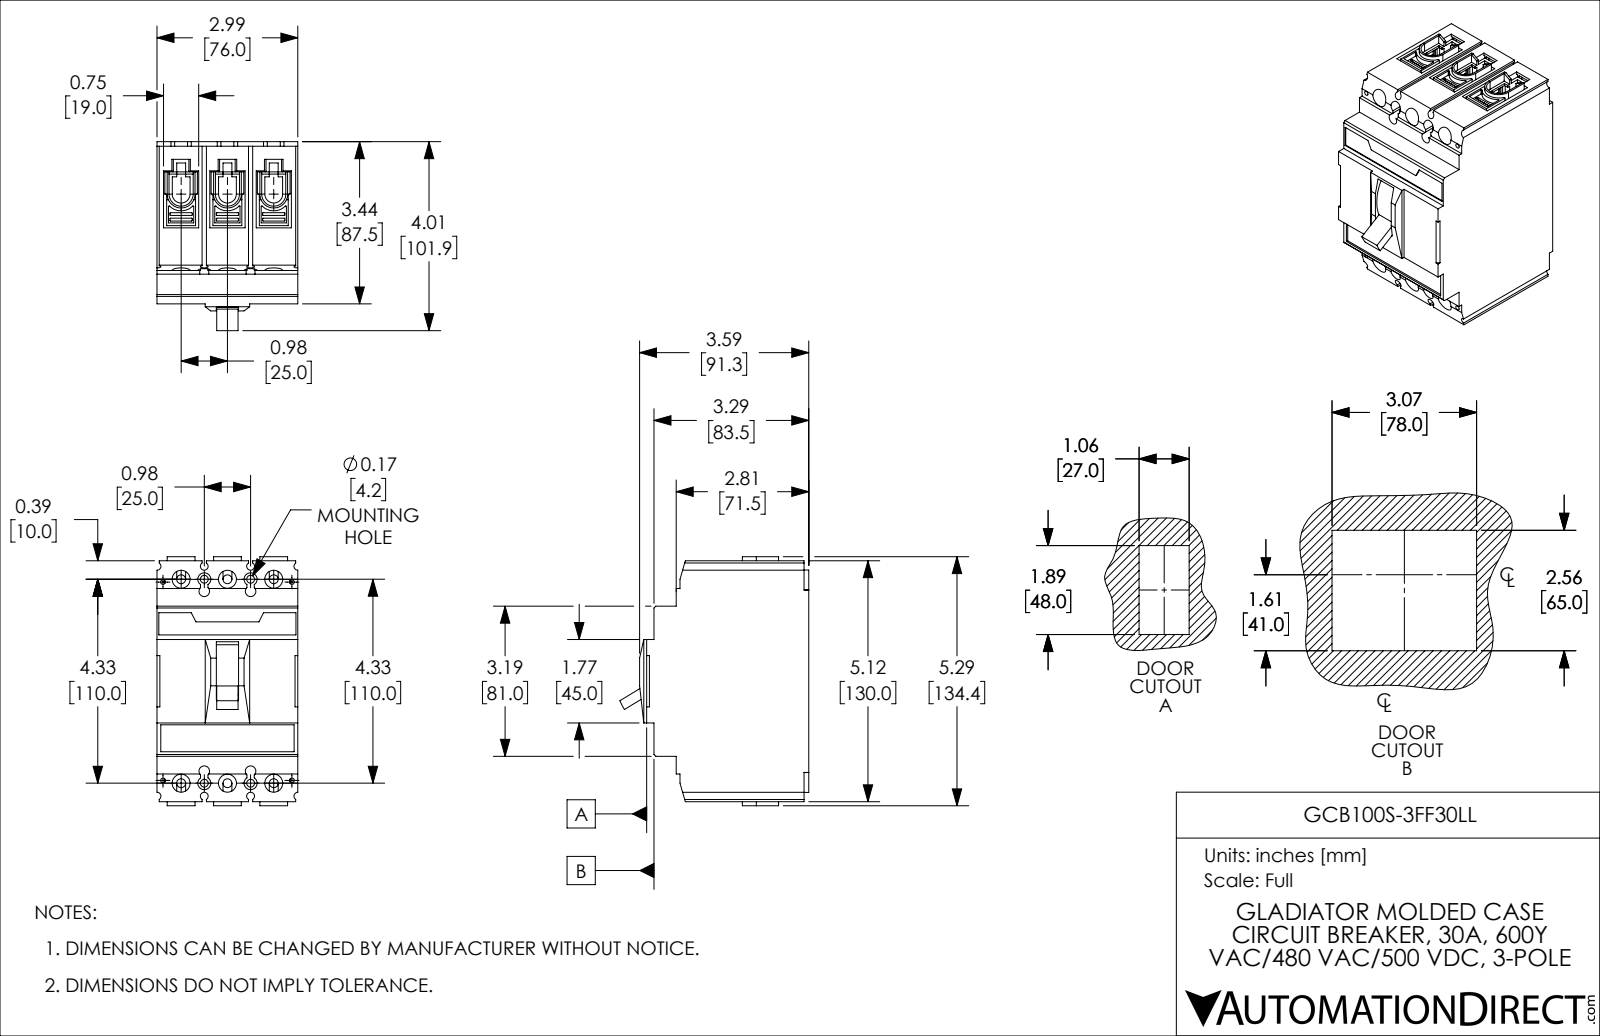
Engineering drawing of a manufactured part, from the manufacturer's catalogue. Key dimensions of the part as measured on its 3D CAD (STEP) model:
Part name (STEP PRODUCT): GCB100S-3FF30LL
STEP written by: SolidWorks 2021 (CONFIG_CONTROL_DESIGN)
Units: inches
Bodies: 1 solid, 1256 faces (784 planar, 424 cylindrical, 48 other)
Overall size (bounding box): 5.291 × 4.013 × 2.992
Volume: 43.23 in³ · Surface area: 148.5 in²
Round holes (diameter × count): ⌀0.165 ×8, ⌀0.189 ×6, ⌀0.382 ×6, ⌀0.098 ×4, ⌀0.276 ×4
Partial cylindrical surfaces — rounded edges, fillets, slot ends (radius × count): R0.012 ×86, R0.02 ×38, R0.039 ×14, R0.157 ×14, R0.024 ×6, R0.083 ×4, R0.112 ×4, R0.189 ×3
Main face-to-face distances: 2.992, 0.984, 0.622, 4.496, 1.732, 0.11, 3.445, 0.748, 1.969, 5.118
Hole centre spacings: 0.492, 0.564, 0.984, 4.359, 4.633, 4.441, 4.331, 0.276
